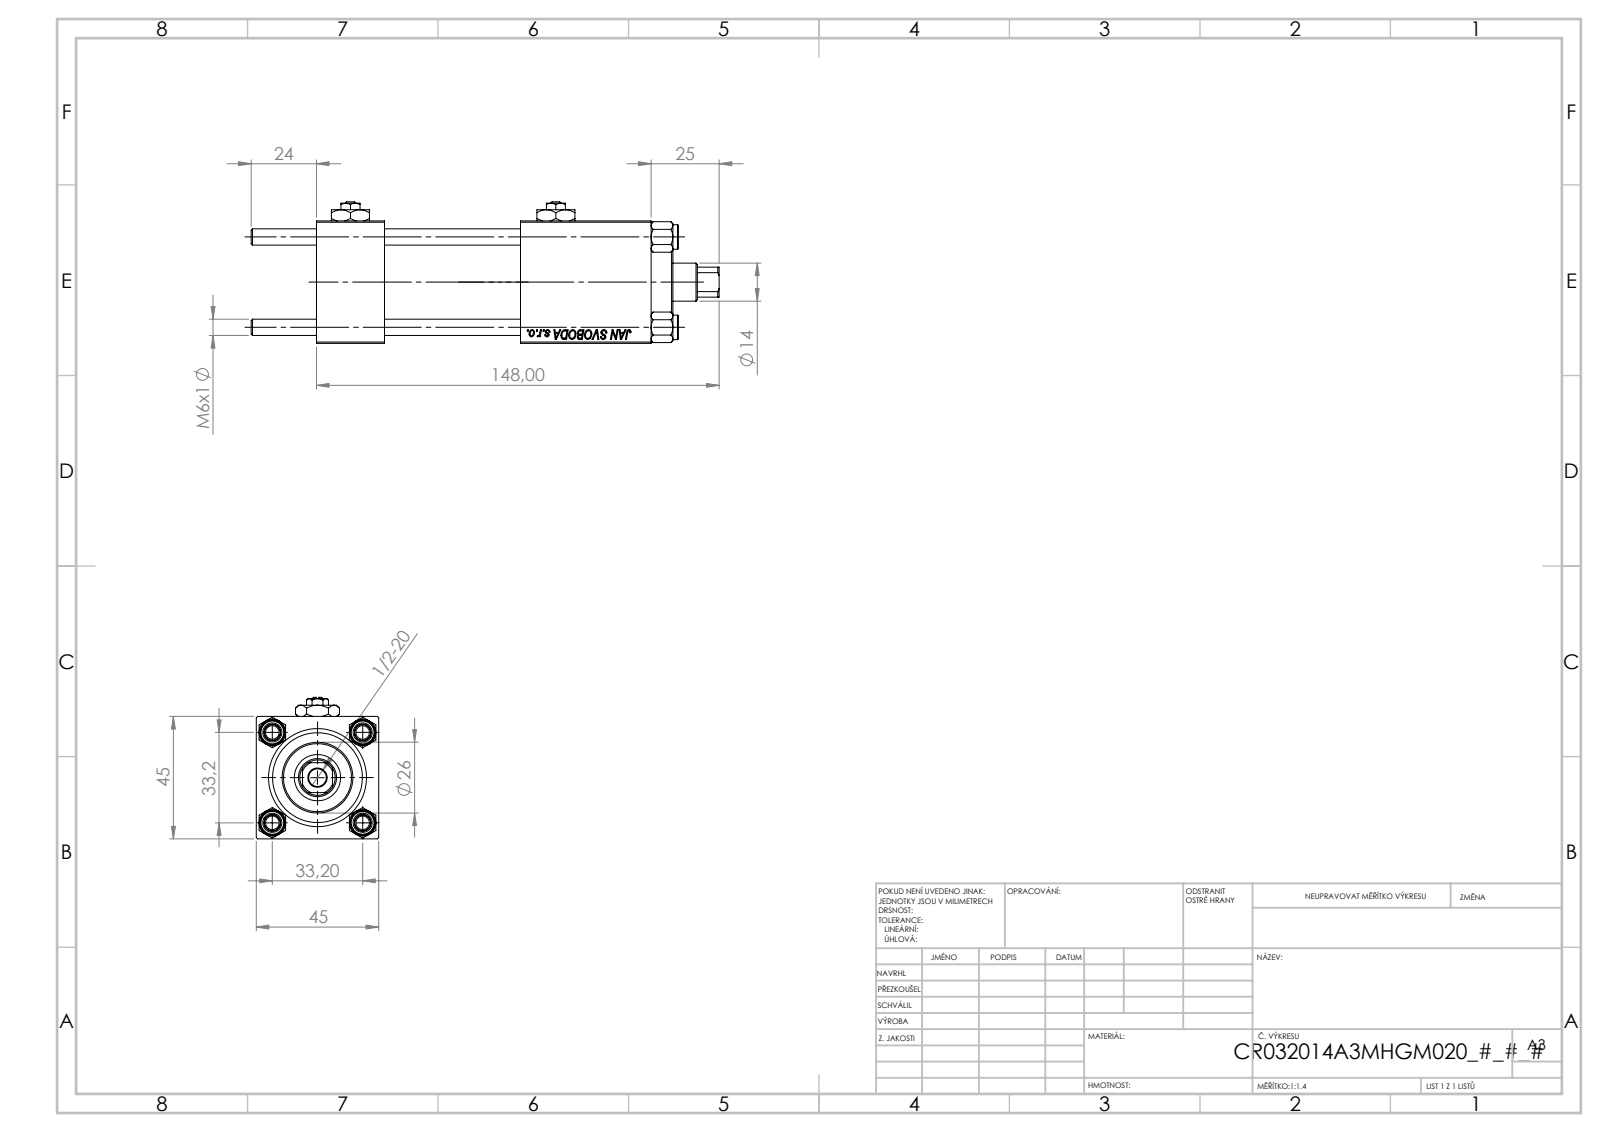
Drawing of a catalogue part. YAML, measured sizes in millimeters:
part_name: "V215CR_BODY_A; CR025_012_A_0_G_A_G_M_020_+#_##_TYCINKA; NUT_M5; V215_VC_A (+2 more)"
step_written_by: "SolidWorks 2019 (CONFIG_CONTROL_DESIGN)"
units: millimeters
bodies: {solids: 13, faces: 1232, planar: 566, cylindrical: 88, other: 578}
overall_size: [172, 52, 45]
volume: 196758
surface_area: 74664
round_holes:
  - {diameter: 6, count: 4}
  - {diameter: 7, count: 2}
  - {diameter: 13.16, count: 2}
  - {diameter: 20, count: 2}
  - {diameter: 6.5, count: 1}
  - {diameter: 14, count: 1}
  - {diameter: 17, count: 1}
  - {diameter: 24, count: 1}
  - {diameter: 32, count: 1}
  - {diameter: 33, count: 1}
round_bosses_or_shafts:
  - {diameter: 9, count: 4}
  - {diameter: 38, count: 1}
  - {diameter: 26, count: 1}
partial_cylinders:
  - {radius: 6.5, count: 1}
face_to_face_distances: [45, 25, 123, 98, 50, 75, 48, 94.3, 69.3, 19.3]
hole_center_spacings: [23.48, 33.2, 46.95, 75.5]
